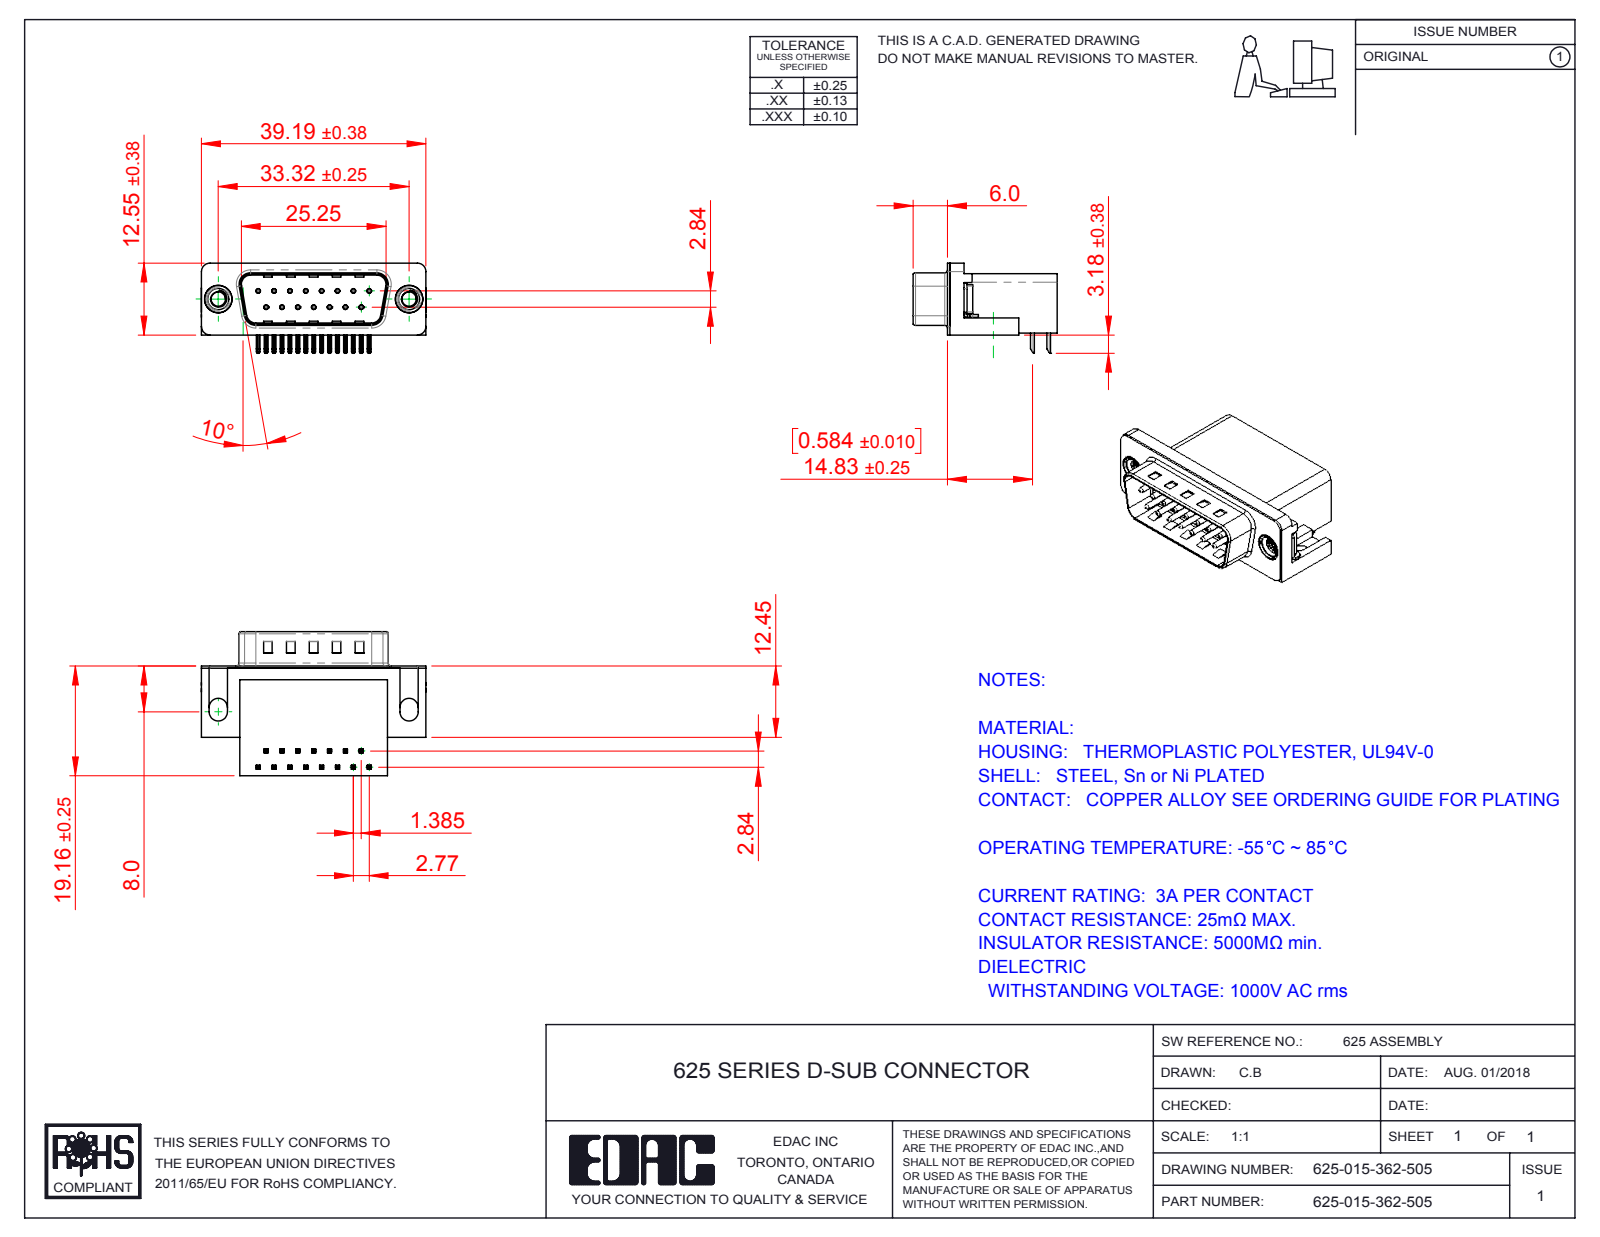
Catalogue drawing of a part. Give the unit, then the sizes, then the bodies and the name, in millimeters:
Units: millimetres
Overall size (bounding box): 39.22 × 25.16 × 15.73
Round holes (diameter × count): ⌀0.35 ×15, ⌀0.8 ×15, ⌀2.5 ×2, ⌀4 ×2, ⌀4.8 ×2, ⌀5 ×2
Round bosses / shafts (diameter × count): ⌀0.75 ×15, ⌀4.9 ×2, ⌀4.75 ×2, ⌀3.9 ×2
Partial cylindrical surfaces — rounded edges, fillets, slot ends (radius × count): R0.25 ×68, R0.12 ×30, R1 ×16, R0.5 ×9, R1.6 ×8, R1.5 ×6, R0.9 ×4, R2 ×4
Main face-to-face distances: 0.4, 10.35, 18.76, 2.1, 10.46, 19.16, 1.7, 10.86, 8.76, 16.26
Hole centre spacings: 3.16, 2.77, 5.54, 8.31, 11.08, 5.03, 5.04, 7.48
Volume: 6 210 mm³ · Surface area: 6 294 mm²
Bodies: 21 solids, 1477 faces (895 planar, 447 cylindrical, 135 other)
Part name (STEP PRODUCT): 625 Contact Top; 625-015-362-505; 625 M3 Threaded Rivet; 625 Non Board Mount (+3 more)
STEP written by: SolidWorks 2016 (CONFIG_CONTROL_DESIGN)
